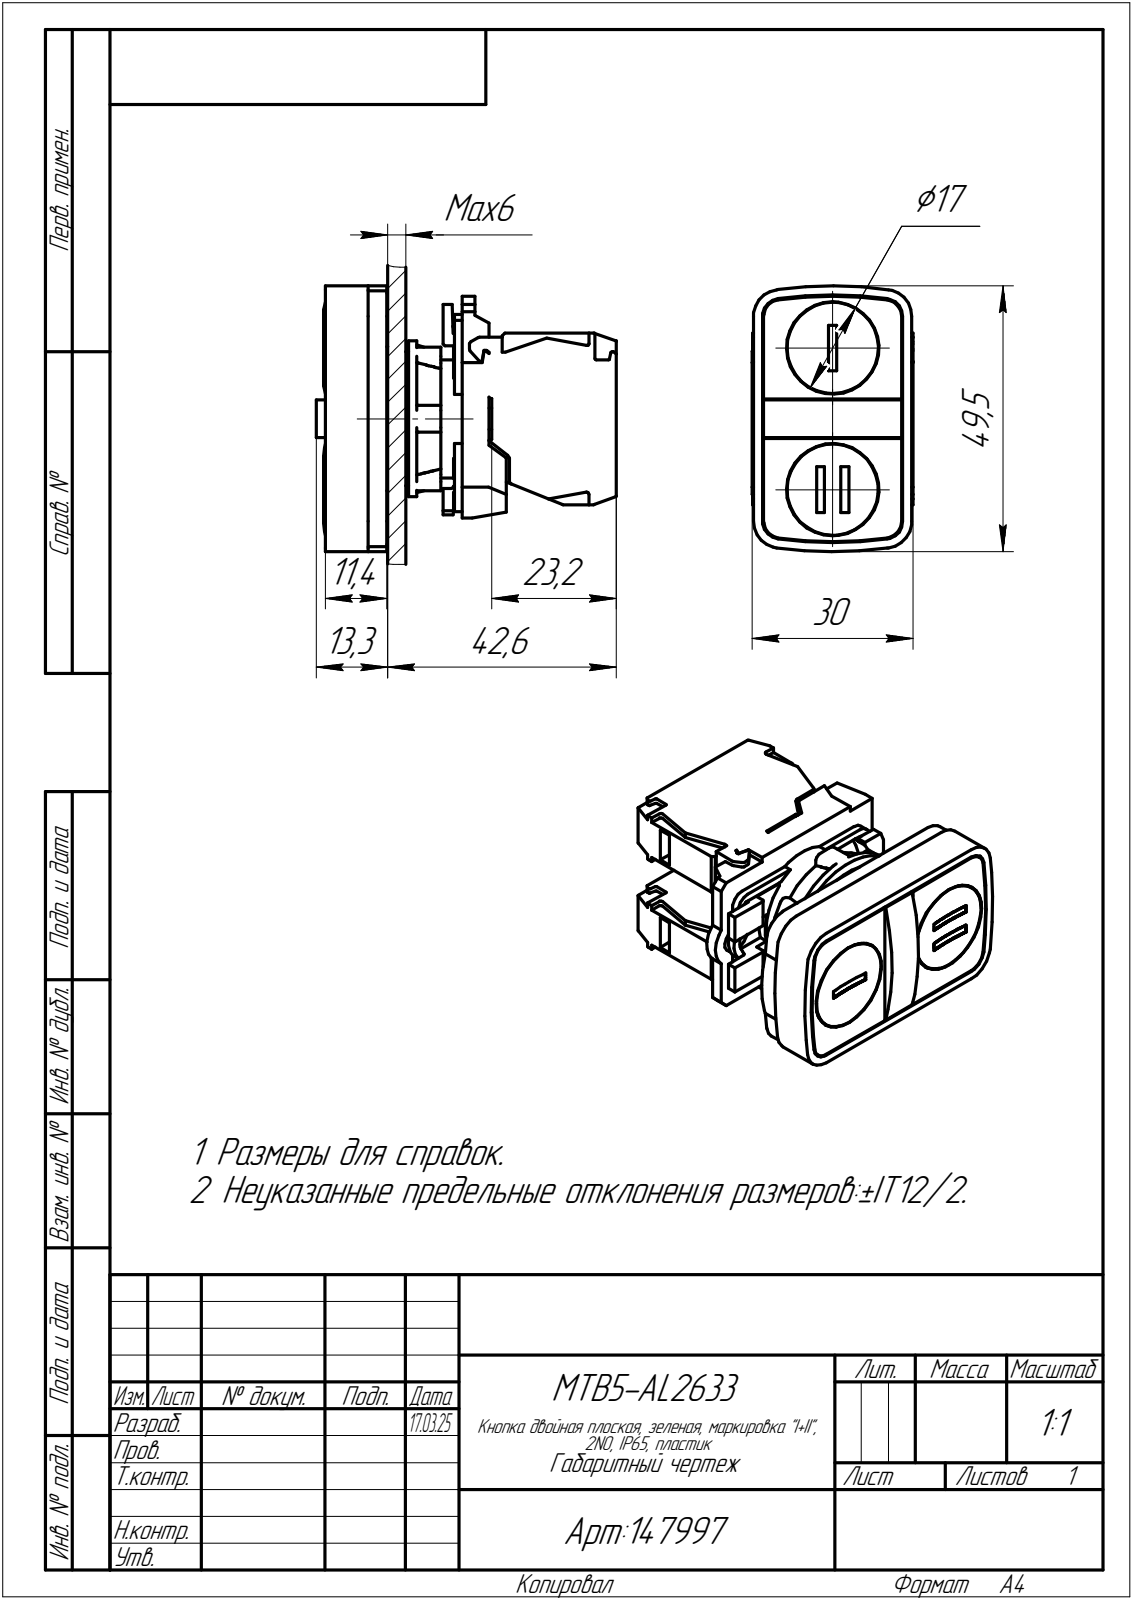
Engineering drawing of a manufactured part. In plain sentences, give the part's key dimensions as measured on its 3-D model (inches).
The part is named "MTB5-AL2633". Its 3-D file was written by "C3D Toolkit (CONFIG_CONTROL_DESIGN)". It is 1 solid with 520 faces: 357 planar, 146 cylindrical and 17 other. Overall it measures 2.201 by 1.949 by 1.181 inches. Its volume is 2.518 cubic inches and its surface area 25.81 square inches. Round holes: 2 of diameter 0.677, 1 of diameter 0.205, 1 of diameter 0.807. Round bosses or shafts: 2 of diameter 0.669, 1 of diameter 1.142, 1 of diameter 1.055, 1 of diameter 0.984, 1 of diameter 0.866. Partial cylindrical surfaces (rounded edges, fillets, slot ends): 15 of radius 0.039, 13 of radius 0.008, 7 of radius 0.02, 4 of radius 0.098, 4 of radius 0.122, 4 of radius 0.13, 4 of radius 0.171, 4 of radius 0.197. The main face-to-face distances are 0.787, 0.39, 0.555, 1.004, 0.449, 0.398, 1.177, 0.354, 1.094, 0.067. The hole center spacings are 0.52, 1.039.
